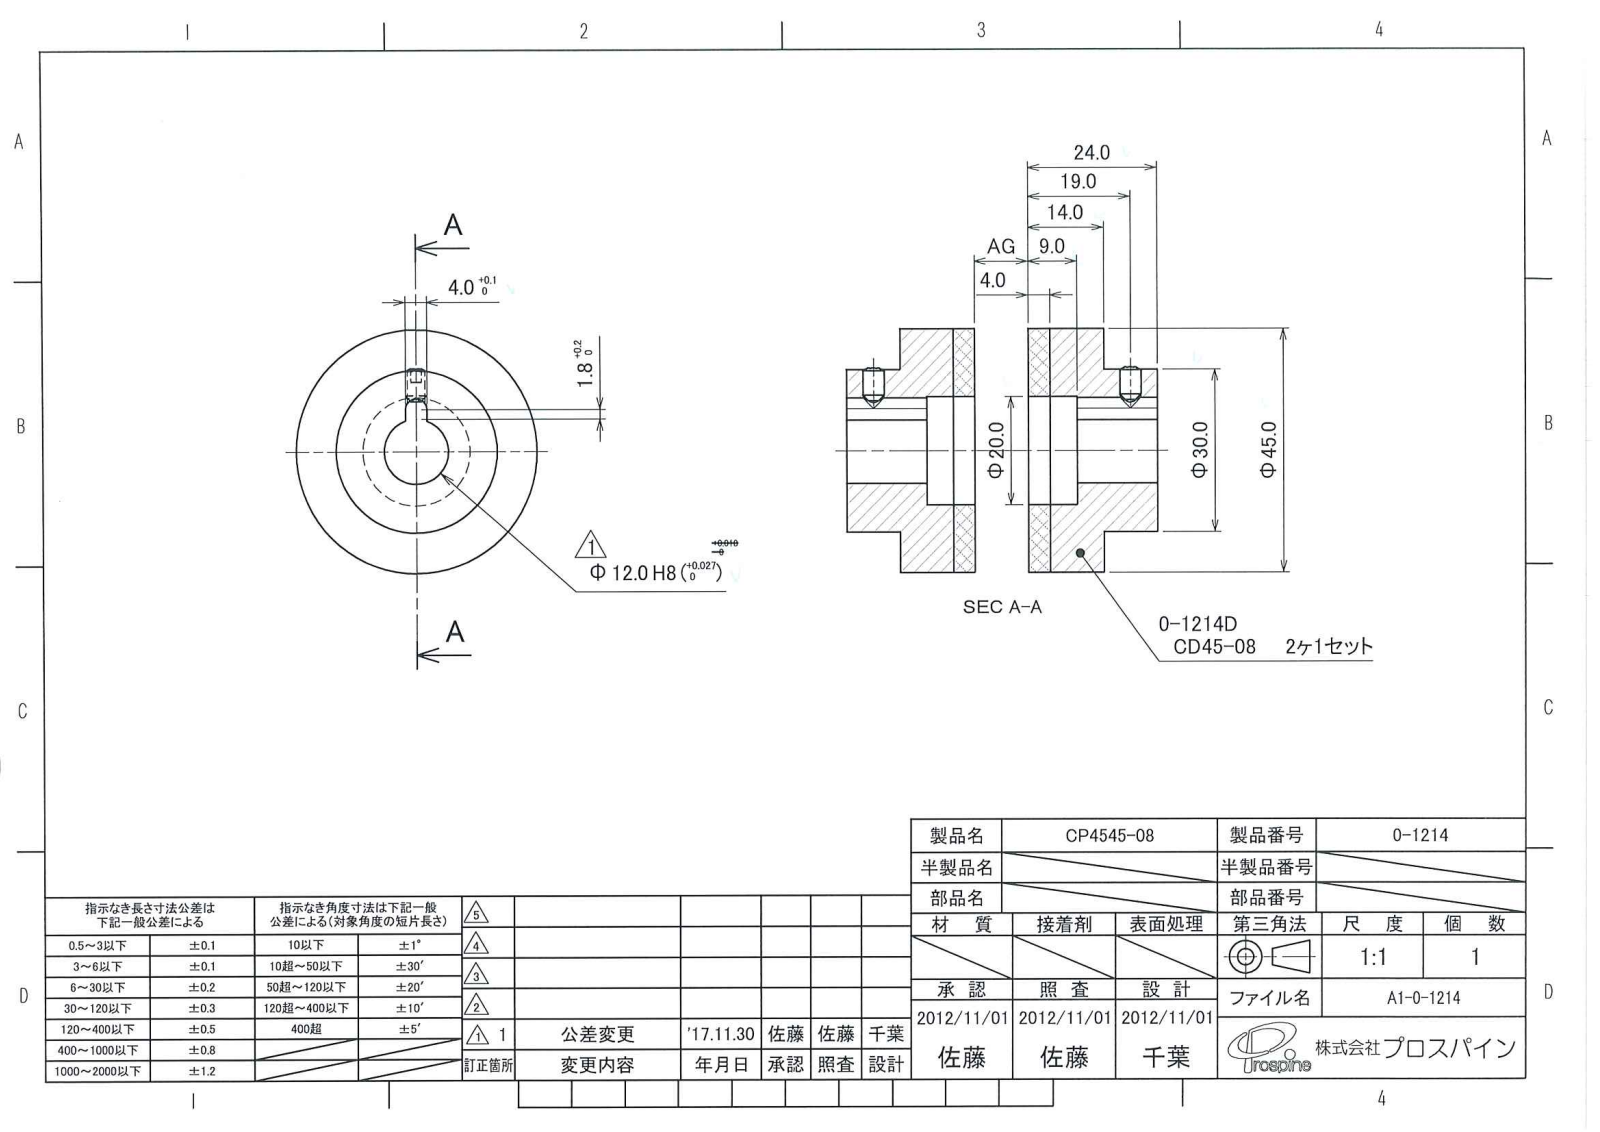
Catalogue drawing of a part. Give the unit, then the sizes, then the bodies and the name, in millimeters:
Units: millimetres
Overall size (bounding box): 45 × 45 × 24
Round holes (diameter × count): ⌀3.3 ×1, ⌀12 ×1, ⌀20 ×1
Round bosses / shafts (diameter × count): ⌀45 ×1, ⌀30 ×1, ⌀4 ×1
Partial cylindrical surfaces — rounded edges, fillets, slot ends (radius × count): R2 ×1
Main face-to-face distances: 10, 4, 14, 24, 20, 5, 9, 15, 2, 1
Volume: 24 672 mm³ · Surface area: 9 877 mm²
Bodies: 4 solids, 38 faces (22 planar, 10 cylindrical, 6 other)
STEP written by: PSStep 10.0 (CONFIG_CONTROL_DESIGN)
